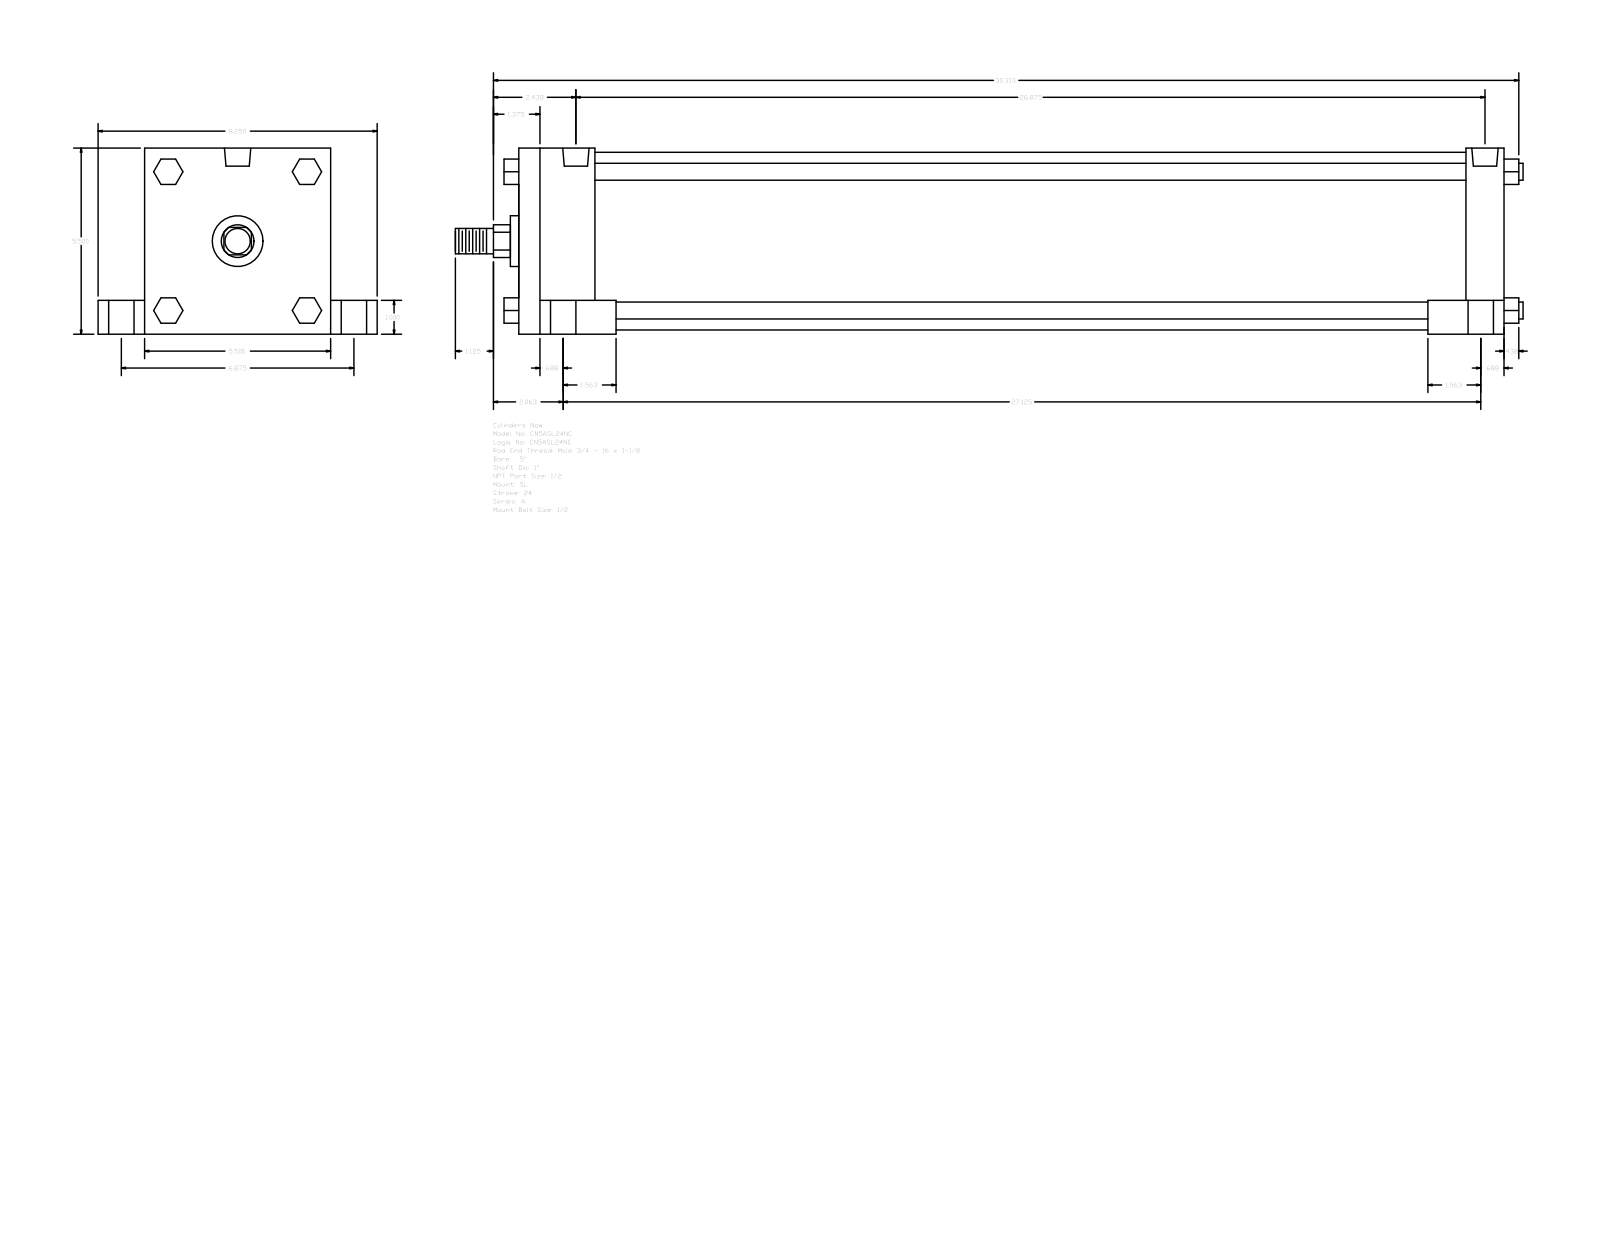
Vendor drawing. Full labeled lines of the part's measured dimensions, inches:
Part name (STEP PRODUCT): A_SL__0500_1
STEP written by: GSSL Pune (CONFIG_CONTROL_DESIGN)
Units: inches
Bodies: 0 solids, 150 faces (114 planar, 36 cylindrical, 0 other)
Overall size (bounding box): 31.563 × 8.25 × 5.5
Round holes (diameter × count): ⌀0.344 ×4, ⌀0.75 ×4, ⌀1 ×4, ⌀0.778 ×2
Round bosses / shafts (diameter × count): ⌀0.5 ×4, ⌀5.25 ×1, ⌀1.5 ×1, ⌀1 ×1, ⌀0.75 ×1
Partial cylindrical surfaces — rounded edges, fillets, slot ends (radius × count): R0.484 ×1
Main face-to-face distances: 5.5, 29.125, 1.125, 1, 4.5, 1.375, 6.875, 2.25, 28, 25.75
Hole centre spacings: 0.094, 3.437, 3.44, 3.458, 3.469, 6.875, 26.687, 26.781
